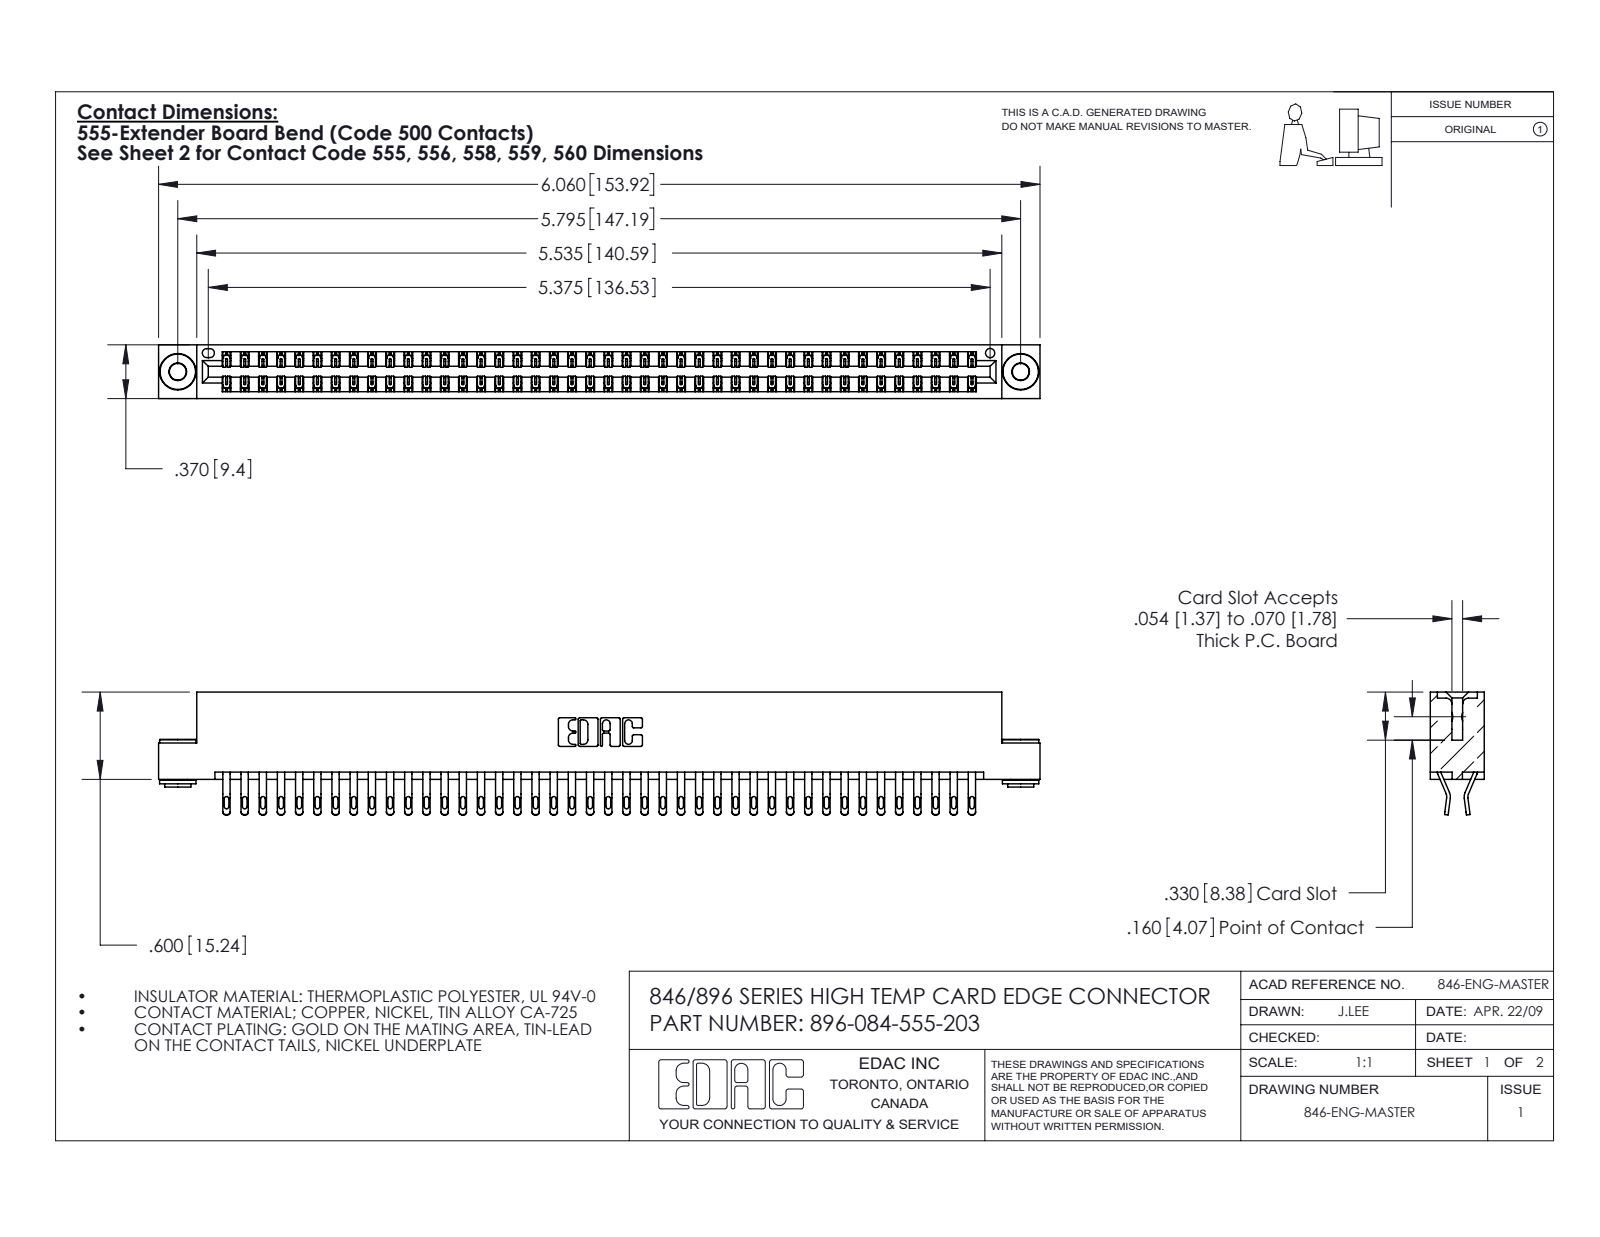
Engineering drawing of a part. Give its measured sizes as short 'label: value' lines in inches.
name: 346 Part_Flush Mounting Lugs - 0.156 Dia-TH; 345-250-002_345-250-002-102; 345-292-001_555 Tail; 396-084-555-203
written by: SolidWorks 2016 (CONFIG_CONTROL_DESIGN)
unit: in
bodies: 87 solids, 5032 faces (2858 planar, 2166 cylindrical, 8 other)
size: 6.06 × 0.845 × 0.37
volume: 0.932 in³; area: 34.22 in²
holes: 2× ⌀0.116, 2× ⌀0.156, 1× ⌀0.064
bosses: 2× ⌀0.25, 2× ⌀0.18, 2× ⌀0.136
rounds: 168× R0.016, 168× R0.02, 126× R0.006, 22× R0.01, 6× R0.007, 6× R0.031, 3× R0.026, 2× R0.01
face distances: 0.048, 0.322, 0.37, 0.25, 0.025, 0.072, 0.298, 0.275, 0.148, 0.222
hole spacings: 0.246, 5.586, 5.795
